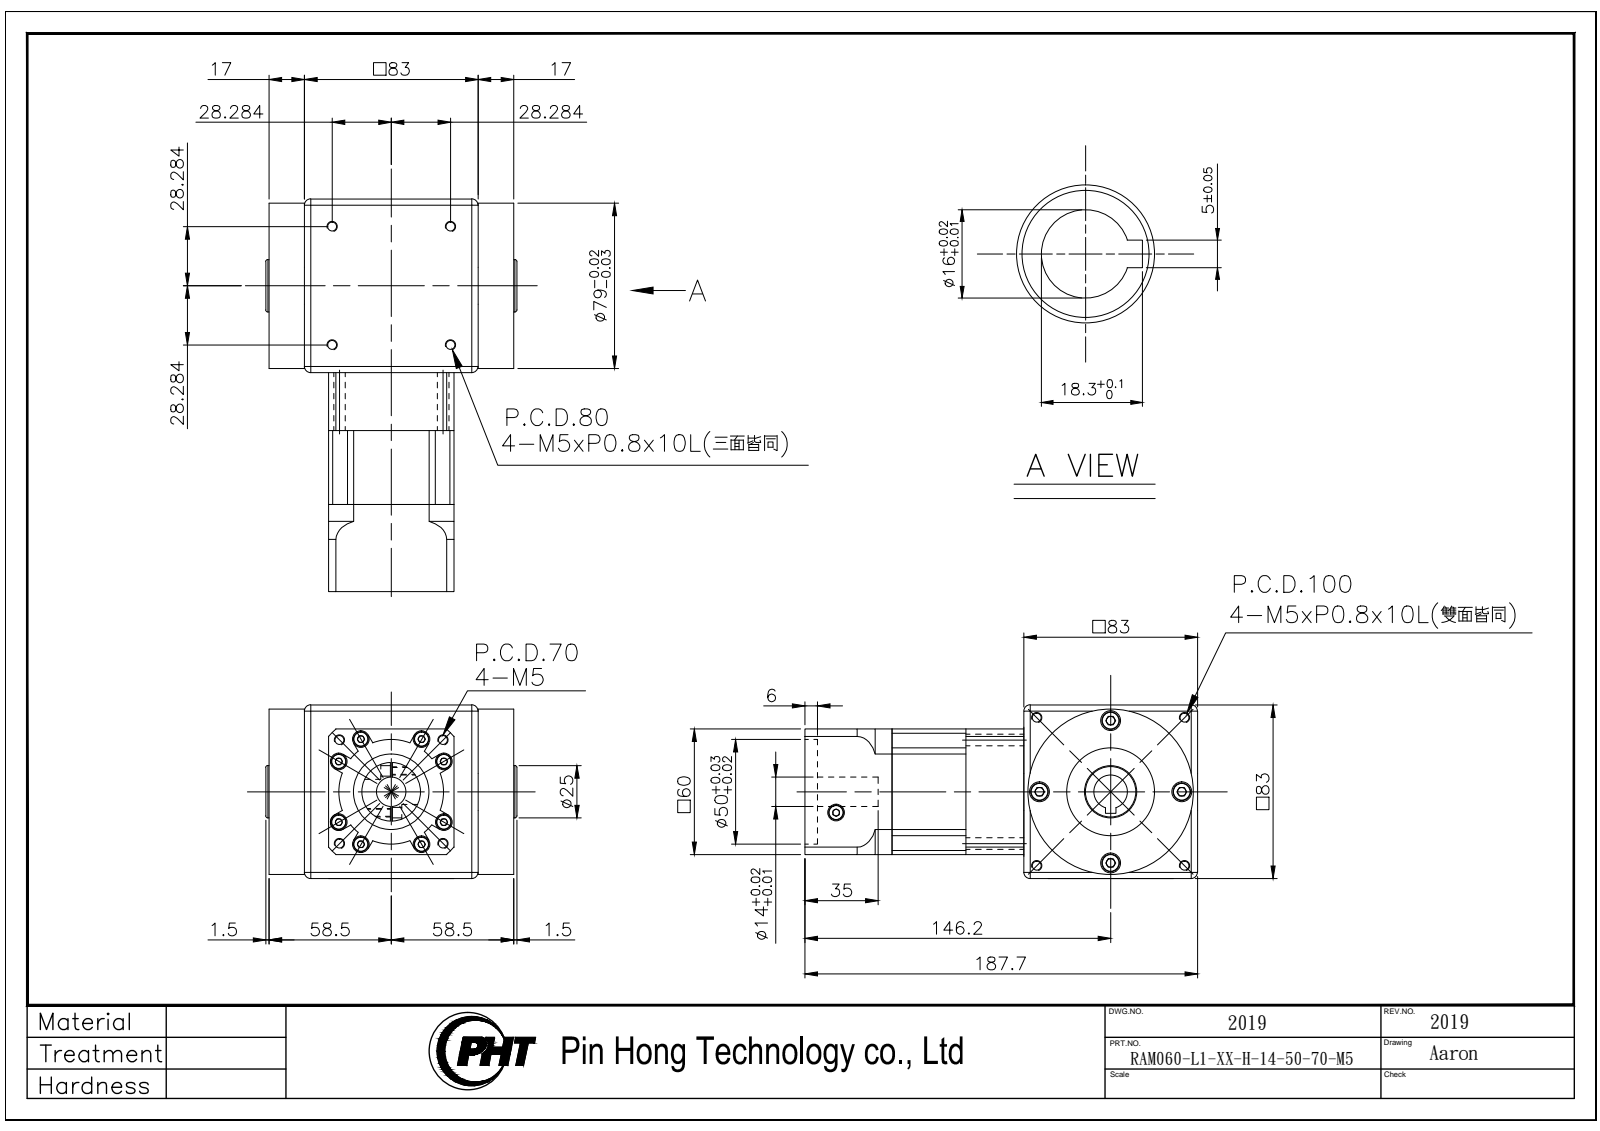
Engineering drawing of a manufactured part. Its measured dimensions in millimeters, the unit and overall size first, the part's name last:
Units: millimetres
Overall size (bounding box): 187.7 × 120 × 83
Round holes (diameter × count): ⌀4.2 ×16, ⌀8 ×10, ⌀4.5 ×8, ⌀5.5 ×8, ⌀9.5 ×4, ⌀14 ×1, ⌀16 ×1, ⌀16.6 ×1, ⌀36 ×1
Round bosses / shafts (diameter × count): ⌀8.5 ×8, ⌀7 ×8, ⌀79 ×1, ⌀55 ×1, ⌀42 ×1, ⌀28 ×1, ⌀25 ×1
Partial cylindrical surfaces — rounded edges, fillets, slot ends (radius × count): R5 ×4, R25 ×1, R35 ×1, R40 ×1, R57.15 ×1
Main face-to-face distances: 83, 11.5, 71.5, 60, 27.7, 35.35, 63.05, 28.5, 88.5, 146.05
Hole centre spacings: 29, 10.26, 14.14, 39.25, 41.01, 42.9, 50.9, 53.15
Volume: 1 022 000 mm³ · Surface area: 127 732 mm²
Bodies: 4 solids, 672 faces (318 planar, 231 cylindrical, 123 other)
Part name (STEP PRODUCT): RAM060-L1-XX-H-14-50-70-M5_2019
STEP written by: SolidWorks 2016 (AUTOMOTIVE_DESIGN)
